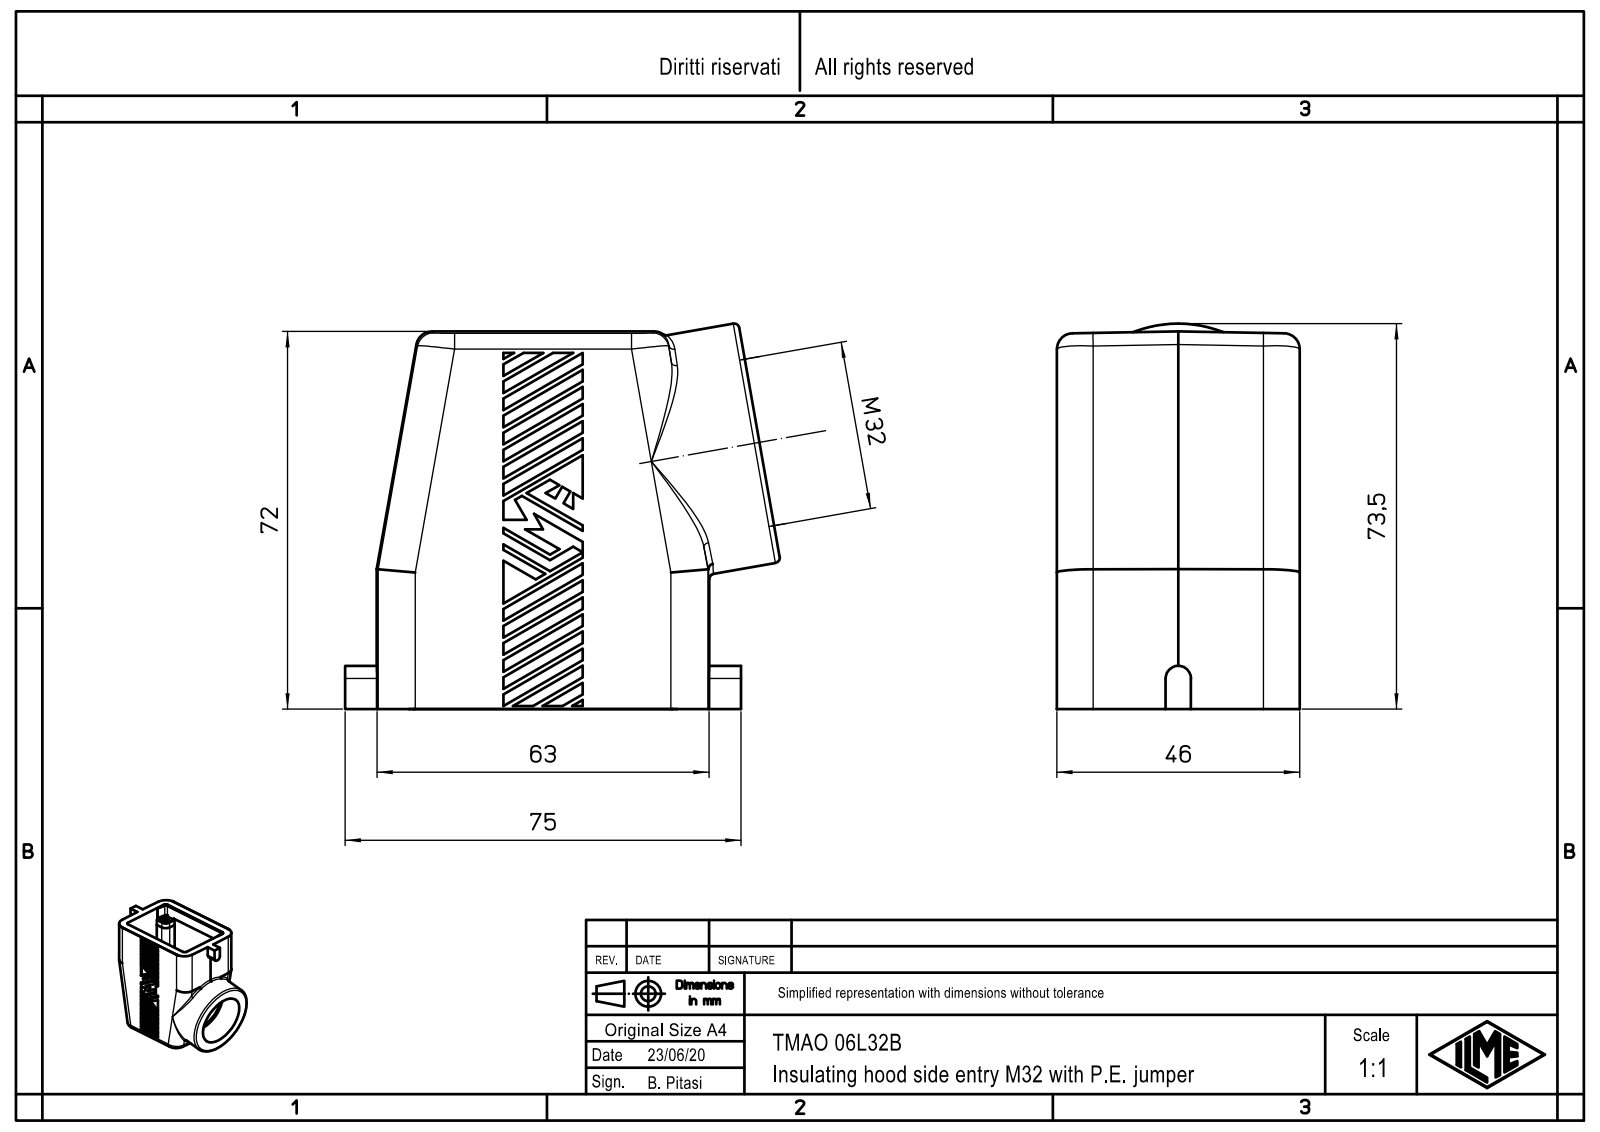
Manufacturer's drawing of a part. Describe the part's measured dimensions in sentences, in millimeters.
The part is named "TMAO_06L32B". Its 3-D file was written by "Creo Elements/Direct Modeling 20.1B 02-Apr-2019 (C) Parametric Technology GmbH (AUTOMOTIVE_DESIGN)". It is 1 solid with 567 faces: 396 planar, 81 cylindrical and 90 other. Overall it measures 82.33 by 72.99 by 46 millimeters. Its volume is 97 538 cubic millimeters and its surface area 35 842 square millimeters. Round holes: 4 of diameter 3, 4 of diameter 3.5, 1 of diameter 28, 1 of diameter 32. Round bosses or shafts: 4 of diameter 4.8, 1 of diameter 46. Partial cylindrical surfaces (rounded edges, fillets, slot ends): 12 of radius 1.5, 8 of radius 7, 6 of radius 3, 4 of radius 1.3, 4 of radius 1.6, 4 of radius 2, 4 of radius 3.5, 1 of radius 2.4. The main face-to-face distances are 46, 0.5, 45.5, 66, 5.6, 63, 6.1, 5.3, 45, 5.8. The hole center spacings are 27, 44, 51.62.
